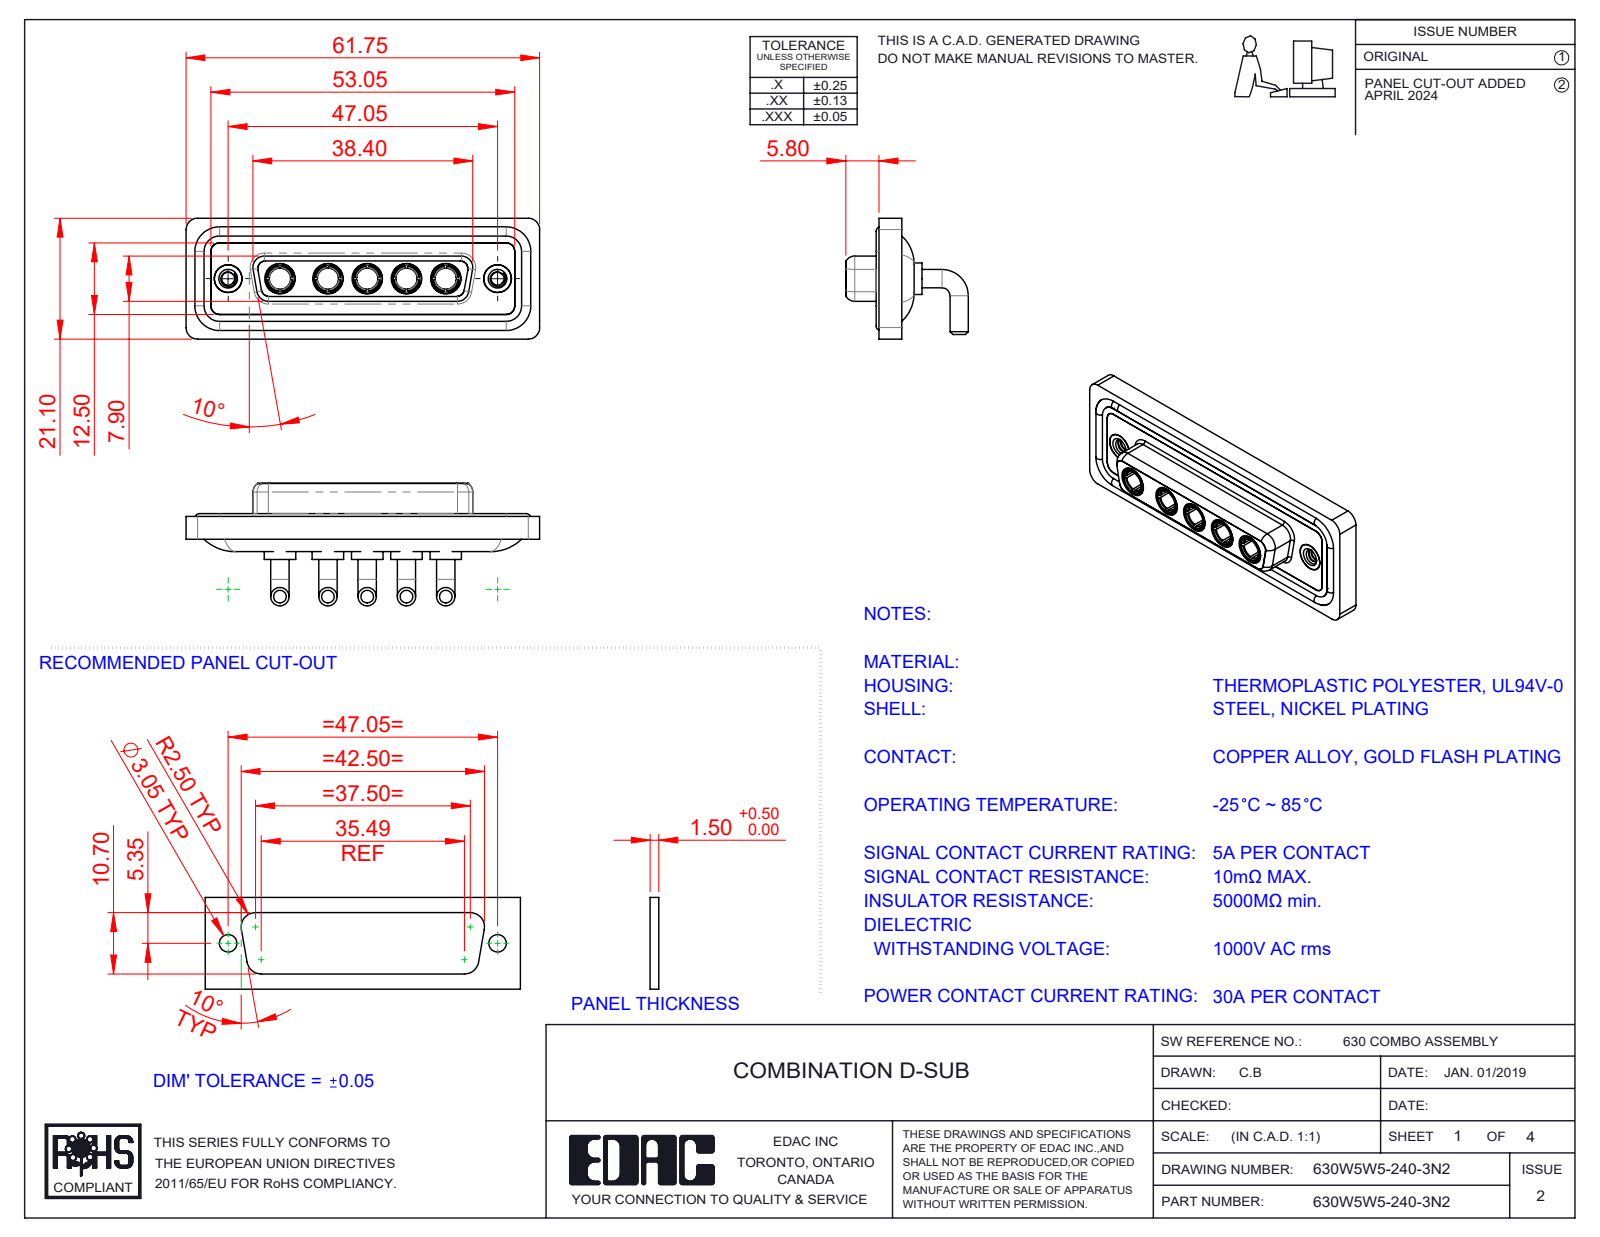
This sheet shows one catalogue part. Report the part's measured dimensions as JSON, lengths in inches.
{"part_name": "630Combo Shell Front_25 Contacts; 630Combo Threaded Rivet_2; 630W5W5-140-3N2; 630Combo Housing_5W5 (+3 more)", "step_written_by": "SolidWorks 2023 (CONFIG_CONTROL_DESIGN)", "units": "inches", "bodies": {"solids": 17, "faces": 776, "planar": 250, "cylindrical": 313, "other": 213}, "overall_size": [2.431, 0.843, 0.831], "volume_in3": 0.523, "surface_area_in2": 21.55, "round_holes": [[0.191, 7], [0.146, 5], [0.209, 5], [0.089, 2], [0.157, 2], [0.159, 2], [0.197, 2]], "round_bosses_or_shafts": [[0.126, 10], [0.217, 5], [0.205, 5], [0.195, 5], [0.187, 5], [0.148, 5], [0.063, 4], [0.195, 2]], "partial_cylinders_radius": [[0.059, 18], [0.079, 18], [0.053, 8], [0.063, 8], [0.083, 5], [0.01, 4], [0.02, 4], [0.024, 4]], "face_to_face_distances": [0.016, 0.071, 0.161, 0.043, 0.059, 0.098, 0.122, 0.146, 0.063, 0.114], "hole_center_spacings": [0.27, 0.356, 1.496, 0.27, 0.33, 0.54, 0.541, 0.6]}
